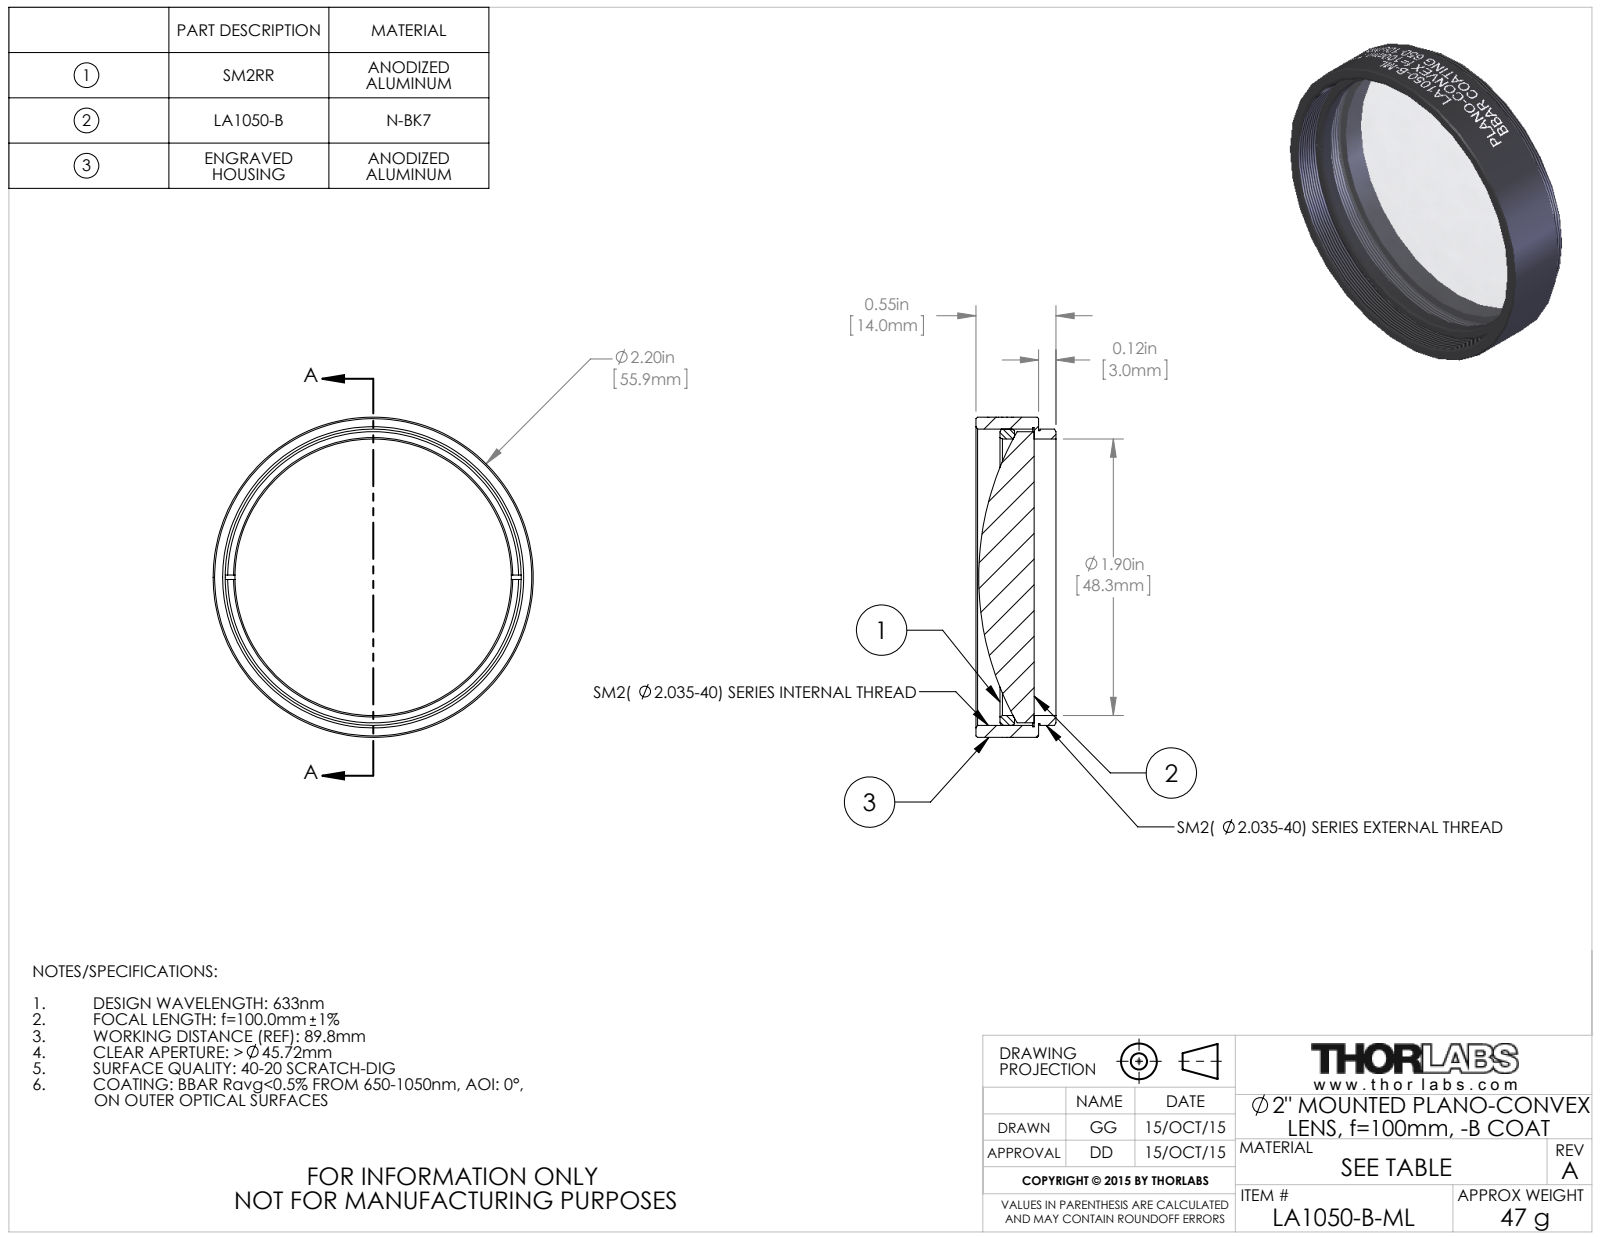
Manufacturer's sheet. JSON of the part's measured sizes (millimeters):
{"part_name": "TTN039493-E0W", "step_written_by": "SolidWorks 2014 (CONFIG_CONTROL_DESIGN)", "units": "millimeters", "bodies": {"solids": 3, "faces": 146, "planar": 16, "cylindrical": 110, "other": 20}, "overall_size": [55.9, 55.9, 14], "volume_mm3": 18500, "surface_area_mm2": 11830, "round_holes": [[48.3, 1], [52.2, 1]], "round_bosses_or_shafts": [[55.9, 1], [51.7, 1], [51.2, 1], [50.8, 1]], "face_to_face_distances": [0.8, 10.9, 10.2, 3, 3.8, 14, 7.3, 4.2, 3.5, 6.7]}
